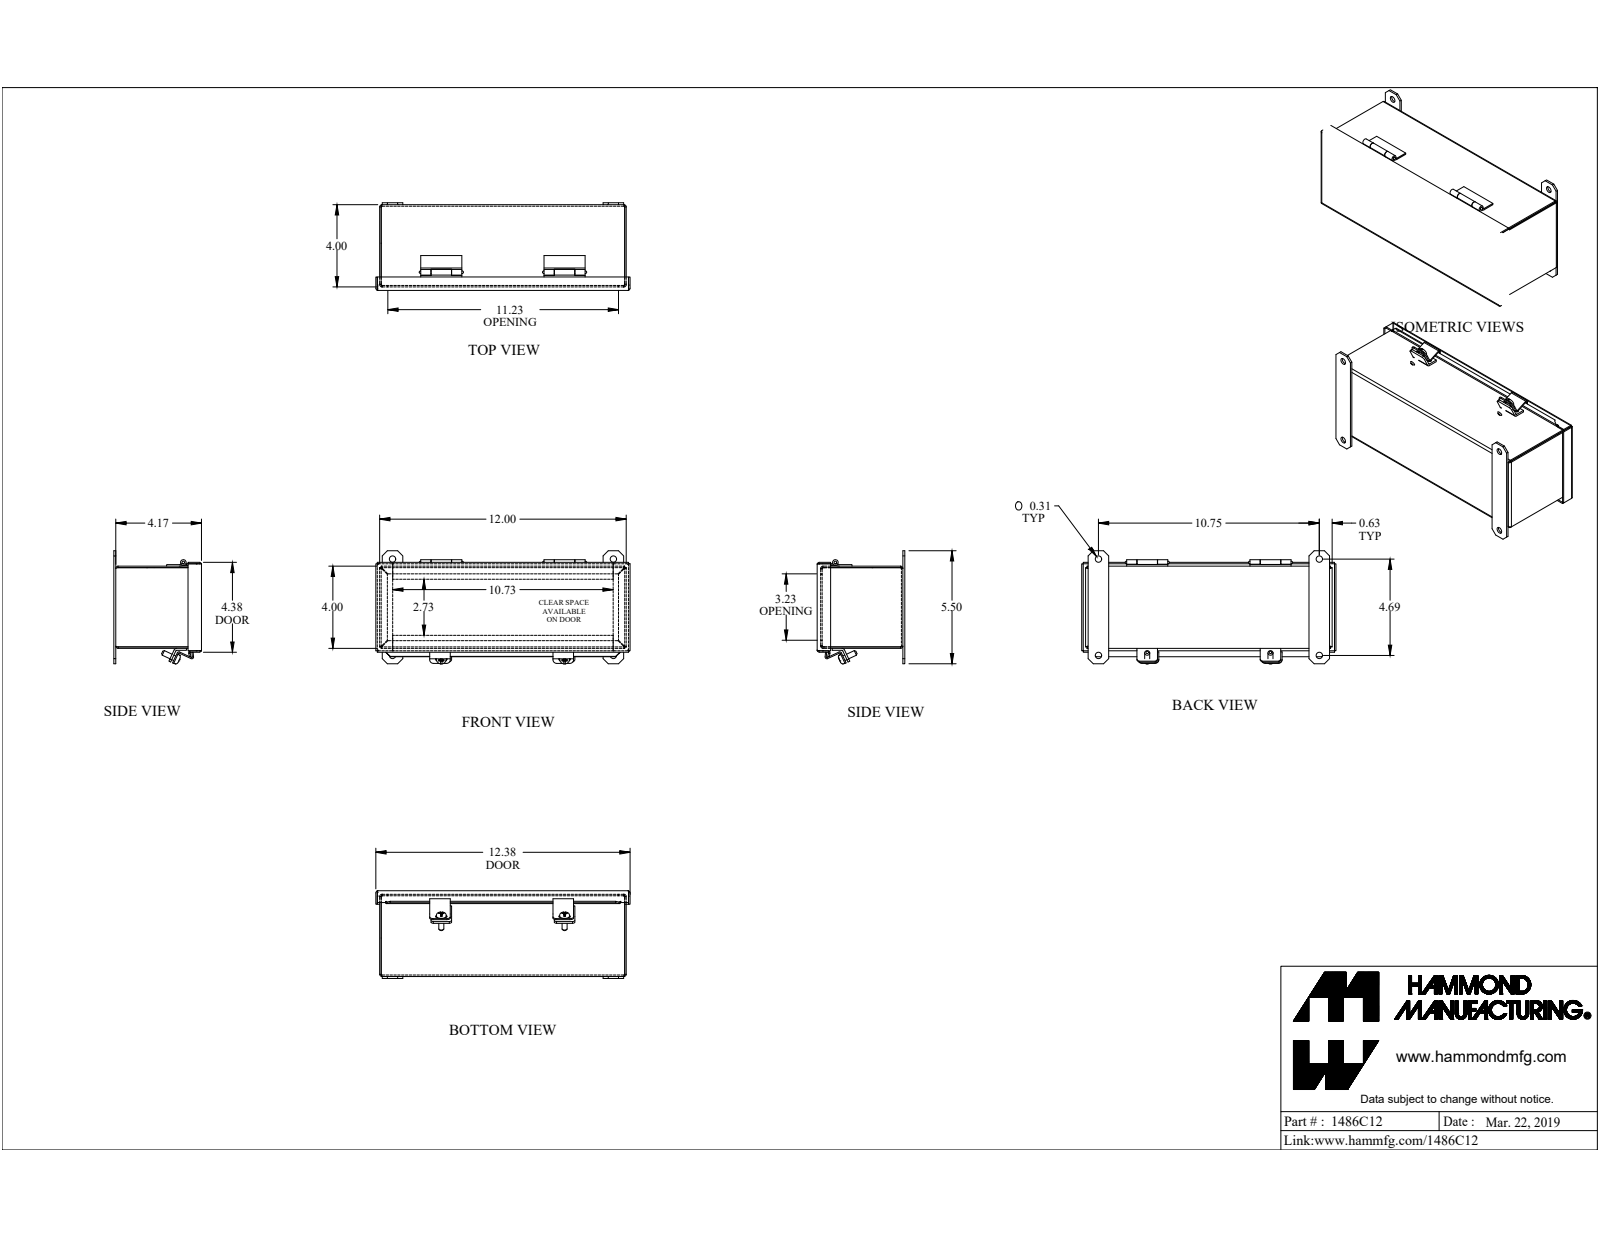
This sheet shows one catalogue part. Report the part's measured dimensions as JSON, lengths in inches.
{"part_name": "1486C12", "step_written_by": "SolidWorks 2019 (CONFIG_CONTROL_DESIGN)", "units": "inches", "bodies": {"solids": 22, "faces": 488, "planar": 325, "cylindrical": 112, "other": 51}, "overall_size": [12.375, 5.506, 4.903], "volume_in3": 24.67, "surface_area_in2": 631.9, "round_holes": [[0.313, 4], [0.213, 2], [0.125, 1]], "round_bosses_or_shafts": [[0.48, 3], [0.246, 3], [0.275, 1]], "partial_cylinders_radius": [[0.036, 13], [0.108, 13], [0.25, 12], [0.188, 10], [0.01, 6], [0.141, 6], [0.029, 4], [0.086, 4]], "face_to_face_distances": [0.072, 3.928, 4.1, 4, 3.856, 4.172, 4.028, 0.187, 11.928, 0.259], "hole_center_spacings": [4.688, 10.75, 11.728, 6]}
